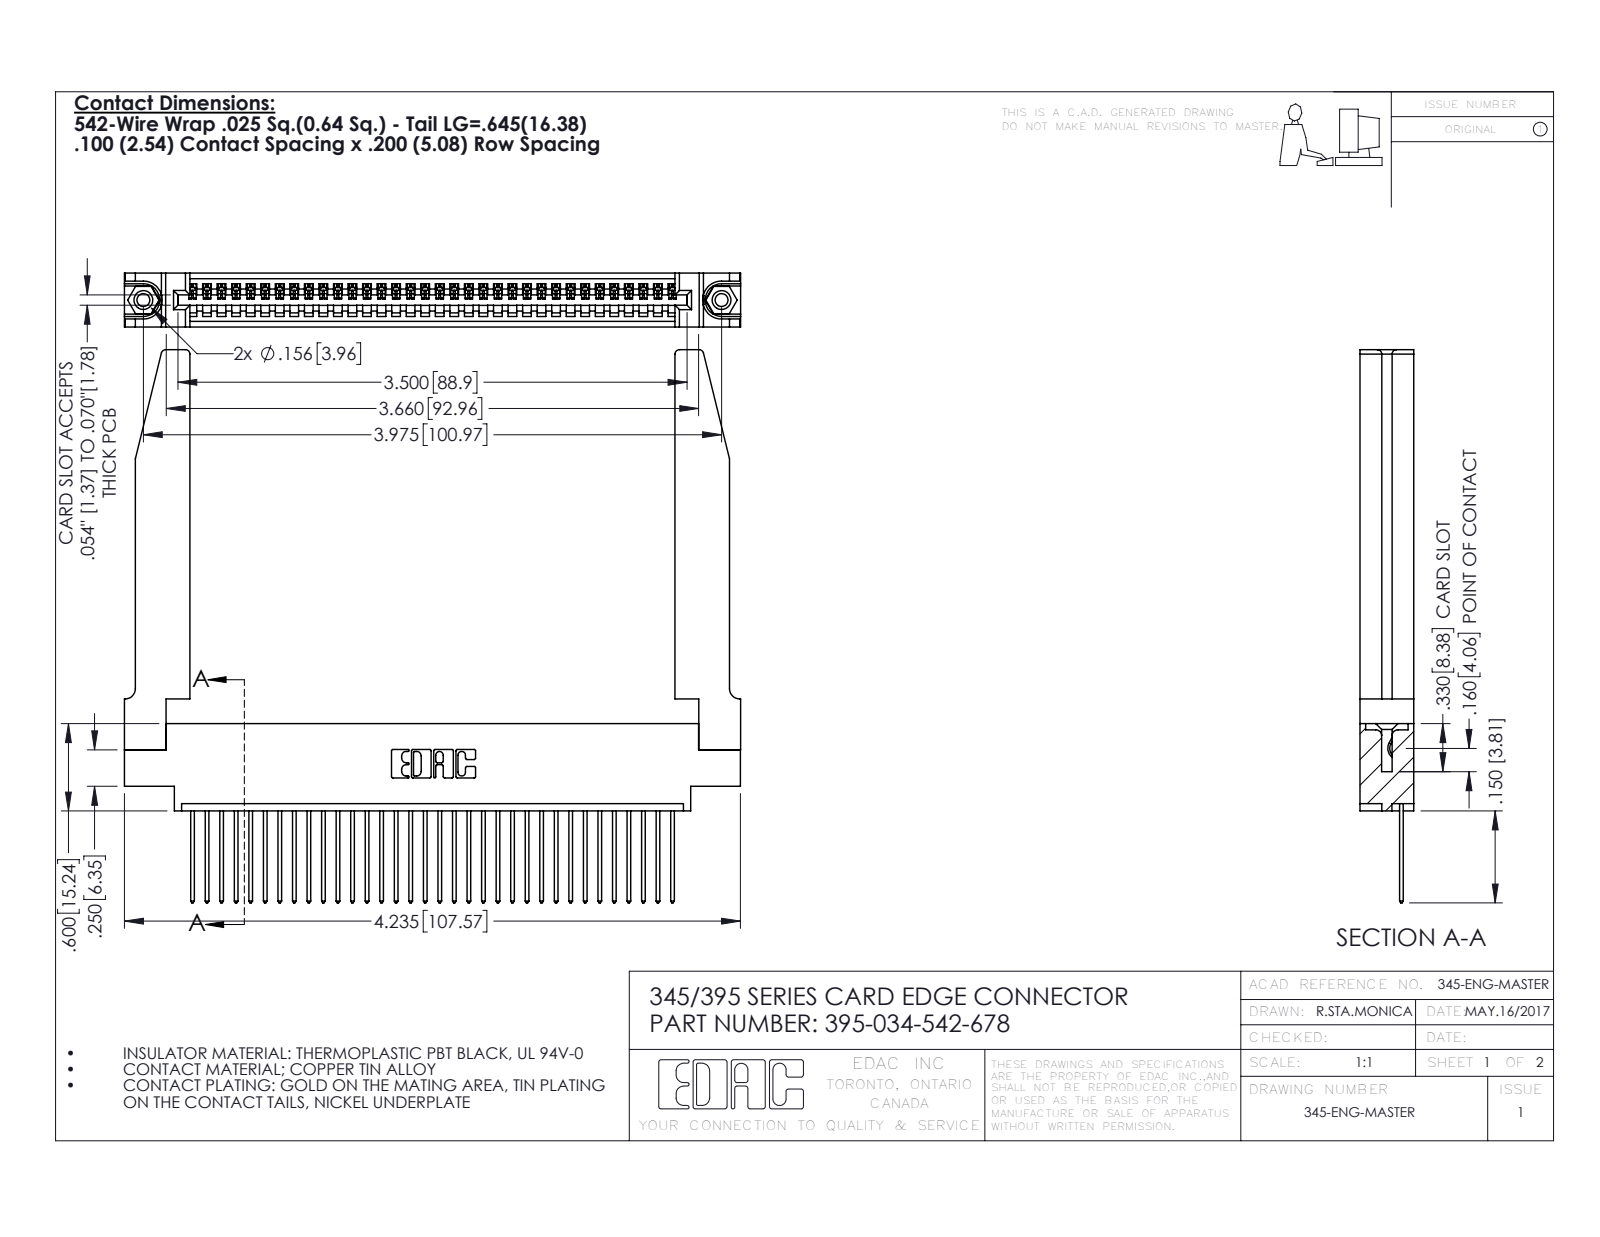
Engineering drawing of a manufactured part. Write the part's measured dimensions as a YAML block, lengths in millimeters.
part_name: "345 Part_0.170 Offset - 0.156 Dia-TH; 395-034-542-678; 345-292-001_345-293-142; 345-250-001_345-250-001-102 (+1 more)"
step_written_by: "SolidWorks 2016 (CONFIG_CONTROL_DESIGN)"
units: millimeters
bodies: {solids: 39, faces: 2336, planar: 1586, cylindrical: 698, other: 52}
overall_size: [107.6, 96.6, 9.4]
volume: 17890
surface_area: 20790
round_holes:
  - {diameter: 2.3, count: 2}
  - {diameter: 3.2, count: 2}
  - {diameter: 4, count: 2}
  - {diameter: 1.6, count: 1}
round_bosses_or_shafts:
  - {diameter: 3.9, count: 2}
partial_cylinders:
  - {radius: 0.2, count: 68}
  - {radius: 0.3, count: 68}
  - {radius: 0.3, count: 22}
  - {radius: 0.8, count: 8}
  - {radius: 0.2, count: 6}
  - {radius: 0.8, count: 6}
  - {radius: 0.7, count: 3}
  - {radius: 0.8, count: 2}
face_to_face_distances: [9.4, 1.8, 7.6, 2.5, 6.9, 0.6, 5.1, 5.7, 3.8, 3.8]
hole_center_spacings: [6.9, 95, 101]
